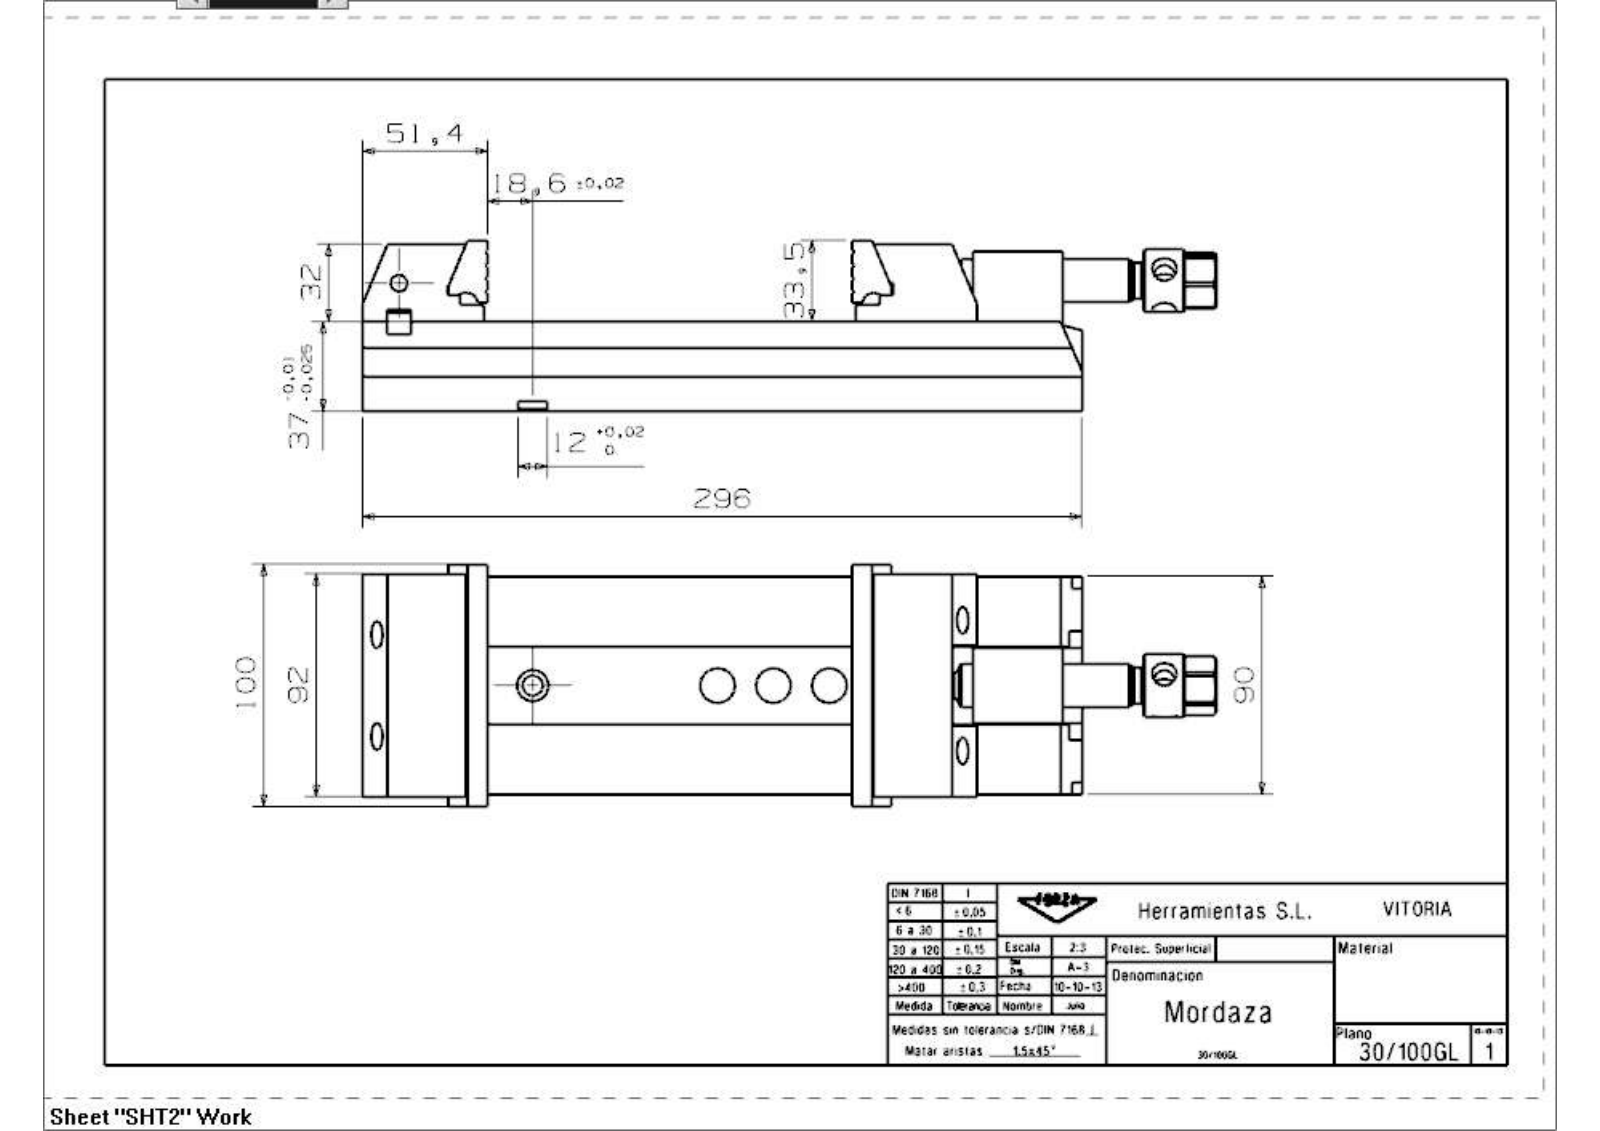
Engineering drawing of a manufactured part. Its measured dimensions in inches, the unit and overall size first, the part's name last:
Units: inches
Overall size (bounding box): 13.828 × 3.937 × 2.776
Round holes (diameter × count): ⌀0.171 ×5, ⌀0.275 ×5, ⌀0.512 ×5, ⌀0.204 ×4, ⌀0.256 ×4, ⌀0.295 ×4, ⌀0.453 ×4, ⌀0.331 ×2, ⌀0.335 ×2, ⌀0.394 ×2, ⌀0.417 ×2, ⌀0.531 ×2
Round bosses / shafts (diameter × count): ⌀1.024 ×1, ⌀0.698 ×1, ⌀0.591 ×1, ⌀0.571 ×1, ⌀0.413 ×1
Partial cylindrical surfaces — rounded edges, fillets, slot ends (radius × count): R0.016 ×16, R0.236 ×5, R0.295 ×4, R0.047 ×2, R0.197 ×2, R0.217 ×2, R0.098 ×1, R0.315 ×1
Main face-to-face distances: 1.457, 0.039, 0.543, 0.913, 1.142, 1.26, 0.197, 0.886, 3.543, 2.657
Hole centre spacings: 1.89, 0.236, 0.237, 1.654, 2.126, 0.436, 0.437, 0.498
Volume: 61.33 in³ · Surface area: 325.3 in²
Bodies: 11 solids, 391 faces (244 planar, 108 cylindrical, 39 other)
Part name (STEP PRODUCT): 30_100L_Mordaza
STEP written by: SIEMENS PLM Software NX 7.5 (AUTOMOTIVE_DESIGN)
